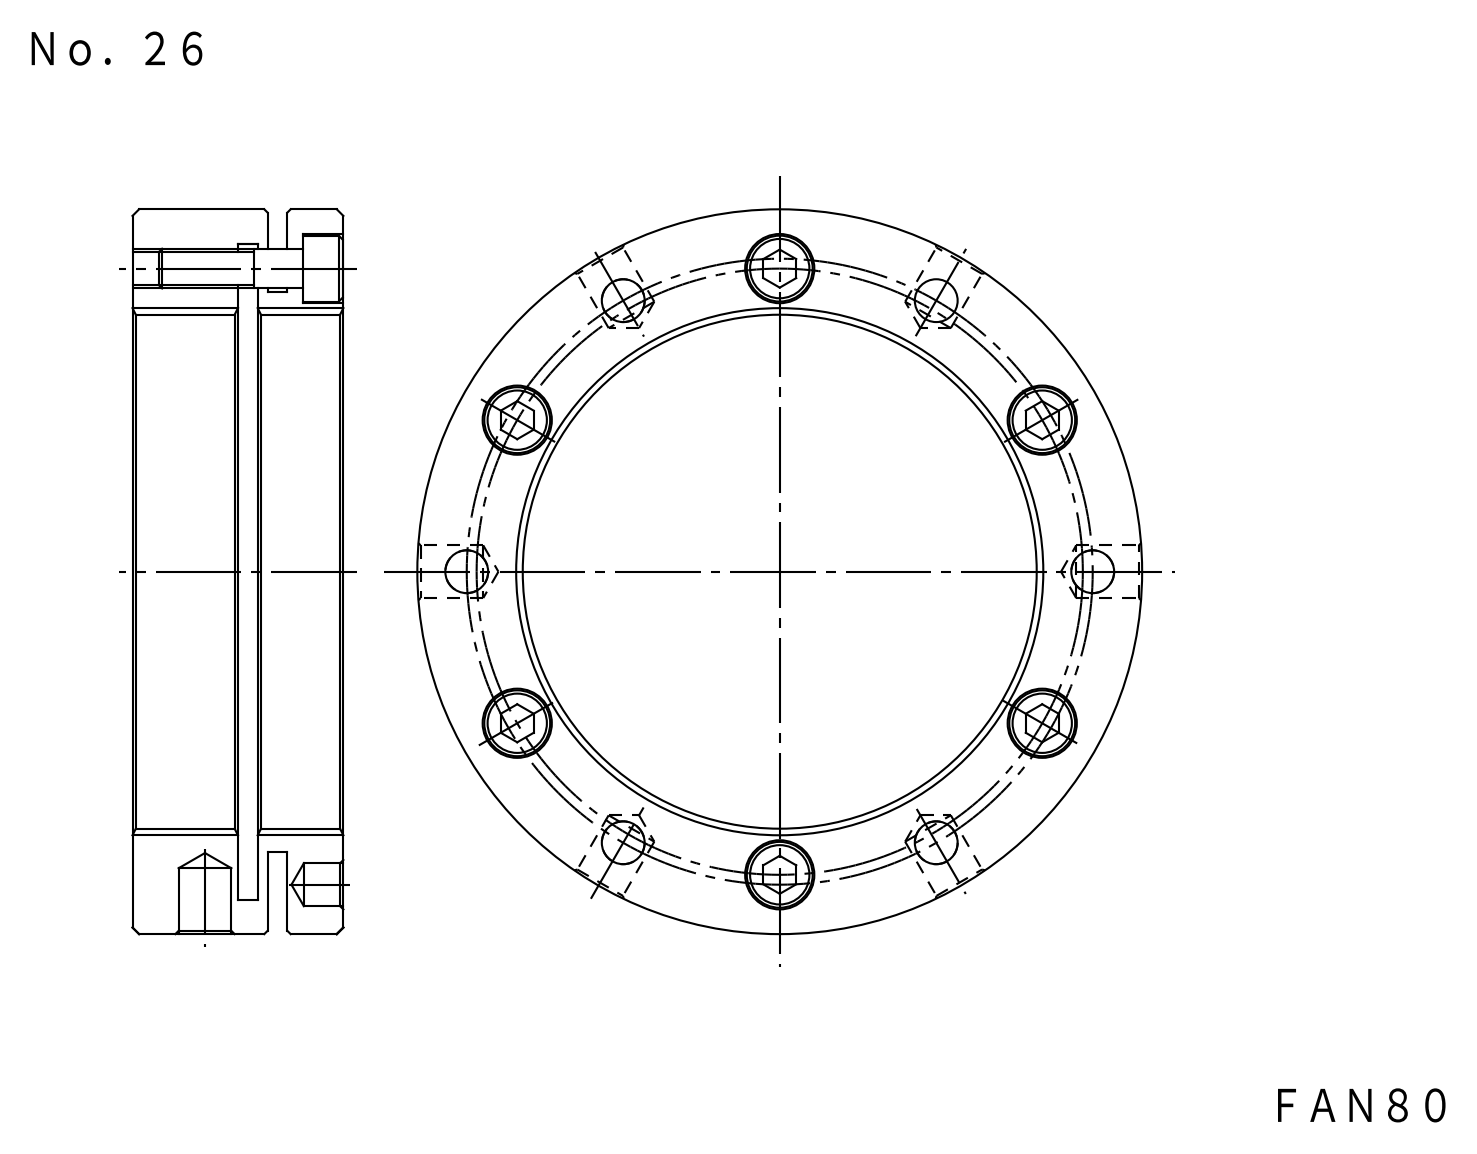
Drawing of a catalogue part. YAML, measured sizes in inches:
part_name: "FKD FAN80; M6X22_default"
step_written_by: "SolidWorks 2012 (CONFIG_CONTROL_DESIGN)"
units: inches
bodies: {solids: 7, faces: 204, planar: 72, cylindrical: 108, other: 24}
overall_size: [4.331, 4.331, 1.26]
volume: 7.523
surface_area: 77.94
round_holes:
  - {diameter: 0.248, count: 6}
  - {diameter: 0.256, count: 6}
  - {diameter: 0.413, count: 6}
  - {diameter: 0.194, count: 3}
  - {diameter: 0.194, count: 3}
  - {diameter: 0.315, count: 3}
  - {diameter: 3.15, count: 1}
  - {diameter: 4.055, count: 1}
round_bosses_or_shafts:
  - {diameter: 0.394, count: 6}
  - {diameter: 0.236, count: 6}
  - {diameter: 4.331, count: 1}
  - {diameter: 3.504, count: 1}
face_to_face_distances: [0.098, 0.157, 1.26, 0.669, 0.591, 0.768, 0.492, 0.827, 0.059, 0.433]
hole_center_spacings: [1.87, 1.89, 2.659, 3.632, 0.973, 3.273, 0.974, 3.239]
